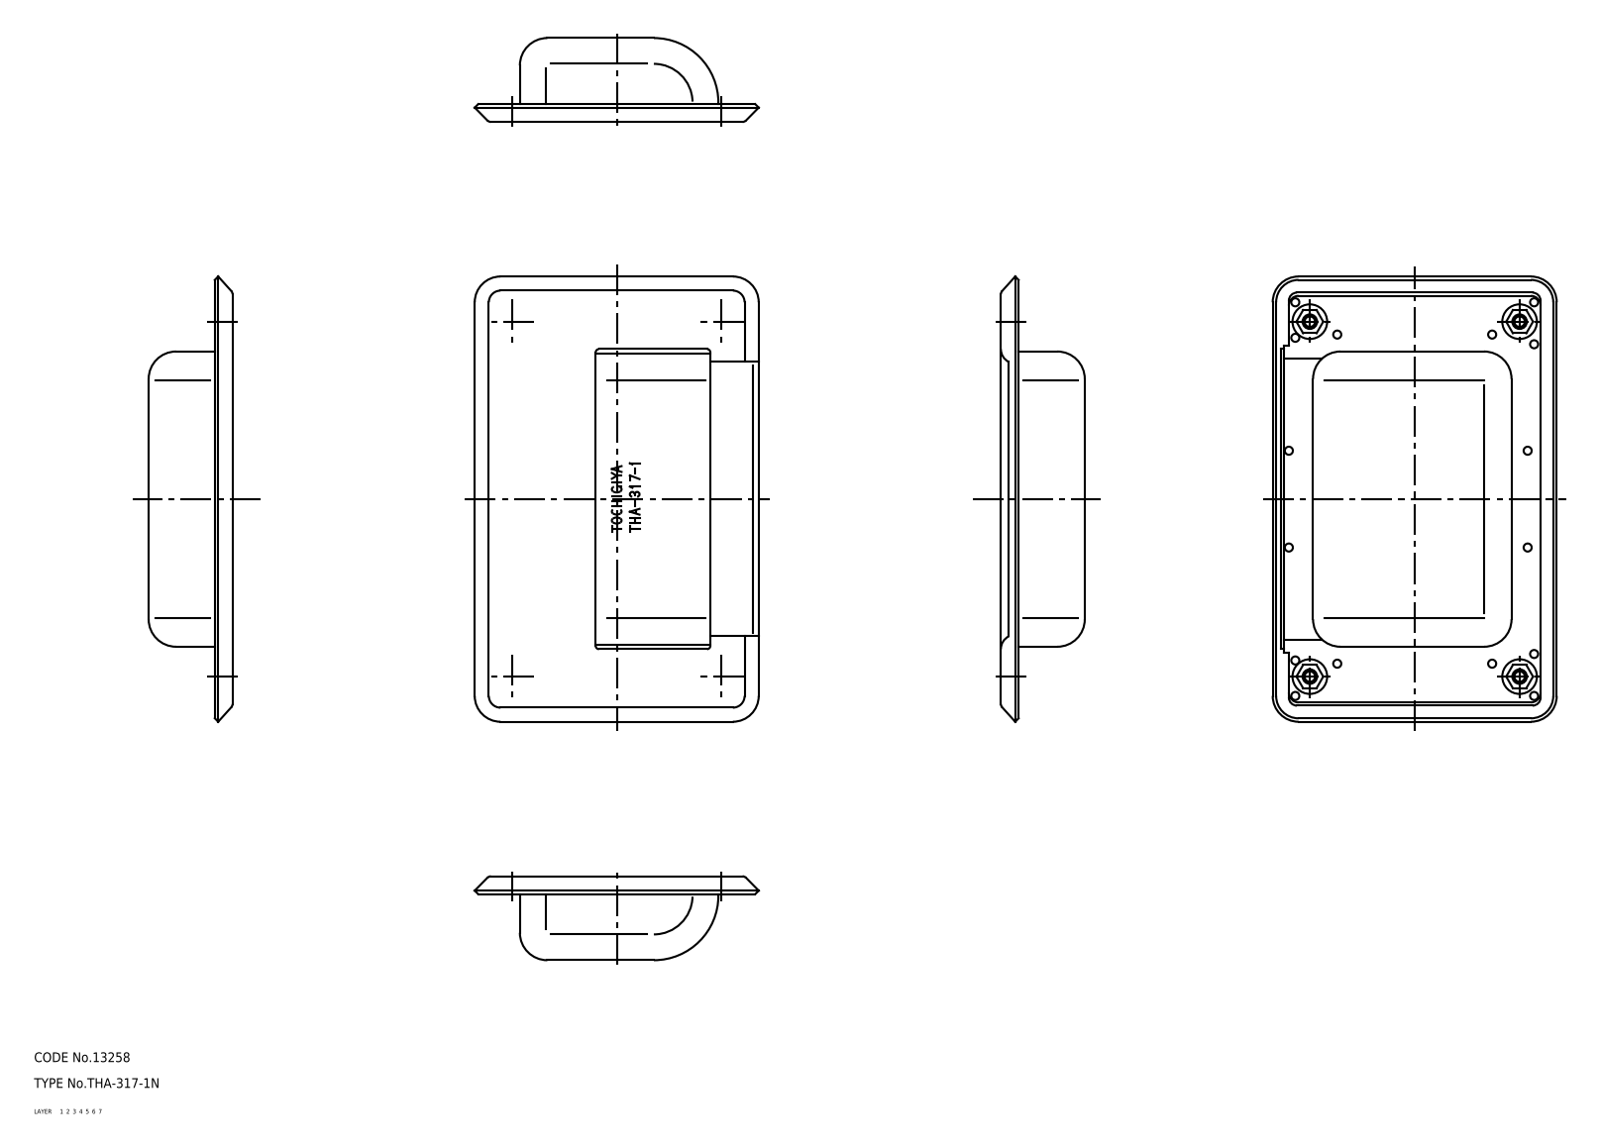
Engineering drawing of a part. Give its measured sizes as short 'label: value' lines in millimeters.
name: nut; cover; base; THA_317_1N_17094_36
written by: CADfix (AUTOMOTIVE_DESIGN)
unit: mm
bodies: 6 solids, 383 faces (0 planar, 0 cylindrical, 383 other)
size: 138 × 88 × 26
volume: 19 046 mm³; area: 53 614 mm²
